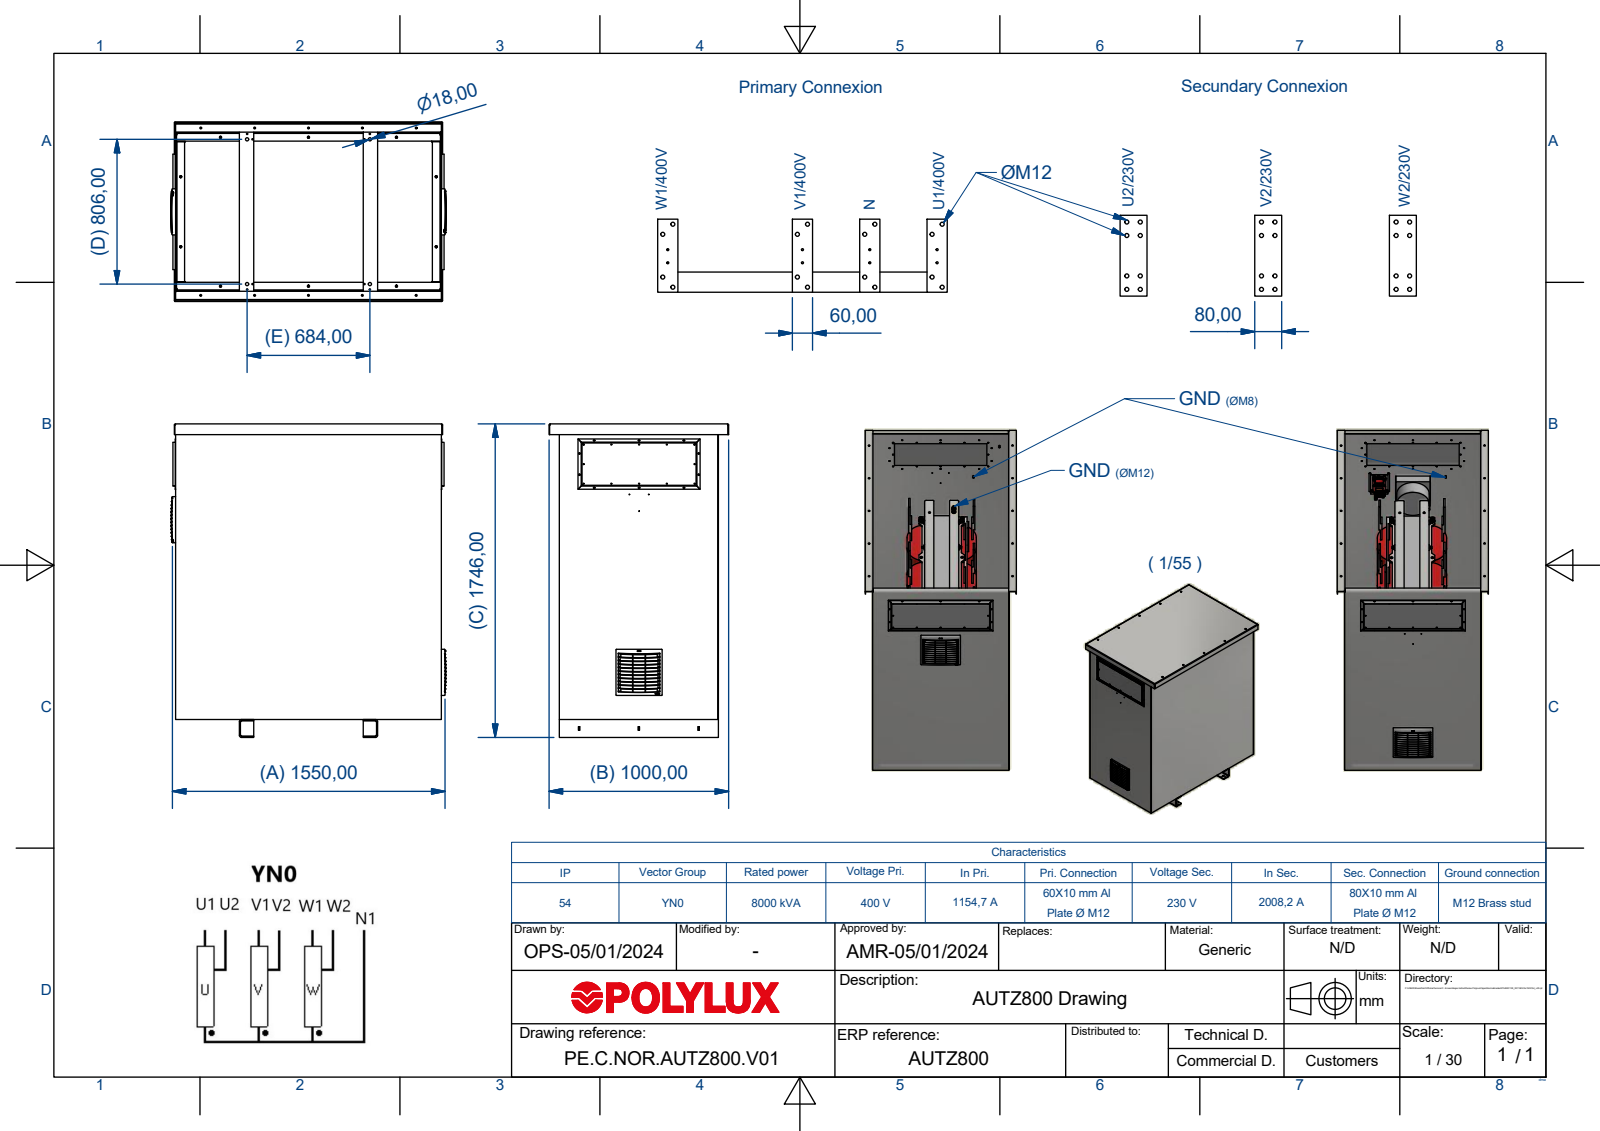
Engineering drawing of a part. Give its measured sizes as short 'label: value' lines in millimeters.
name: CAJ150C54_Nueva; Base_CAJ150C54_A; Cuerpo_CAJ150C54-(lado prensaestopa)_A; Cuerpo_CAJ150C54 (+8 more)
written by: Autodesk Inventor 2008 (AUTOMOTIVE_DESIGN)
unit: mm
bodies: 29 solids, 2895 faces (1162 planar, 762 cylindrical, 971 other)
size: 1762 × 1446.2 × 870
volume: 23 130 000 mm³; area: 19 970 000 mm²
holes: 10× ⌀12, 10× ⌀18, 8× ⌀17, 6× ⌀16.5, 4× ⌀11, 4× ⌀11.2, 4× ⌀20, 3× ⌀3.5, 2× ⌀35, 2× ⌀45, 2× ⌀53.5, 2× ⌀61
bosses: 10× ⌀16, 6× ⌀26.5, 6× ⌀22.49, 4× ⌀14.8, 2× ⌀77.5, 2× ⌀72, 2× ⌀63, 2× ⌀59.5
rounds: 182× R0.2, 114× R0.3, 43× R0.15, 25× R0.5, 24× R6, 8× R2, 8× R7, 7× R4
face distances: 2, 710, 1378, 712, 708, 3, 1380, 1376, 1650, 1647
hole spacings: 300, 805.92, 600, 690, 958.91, 748, 61, 114
